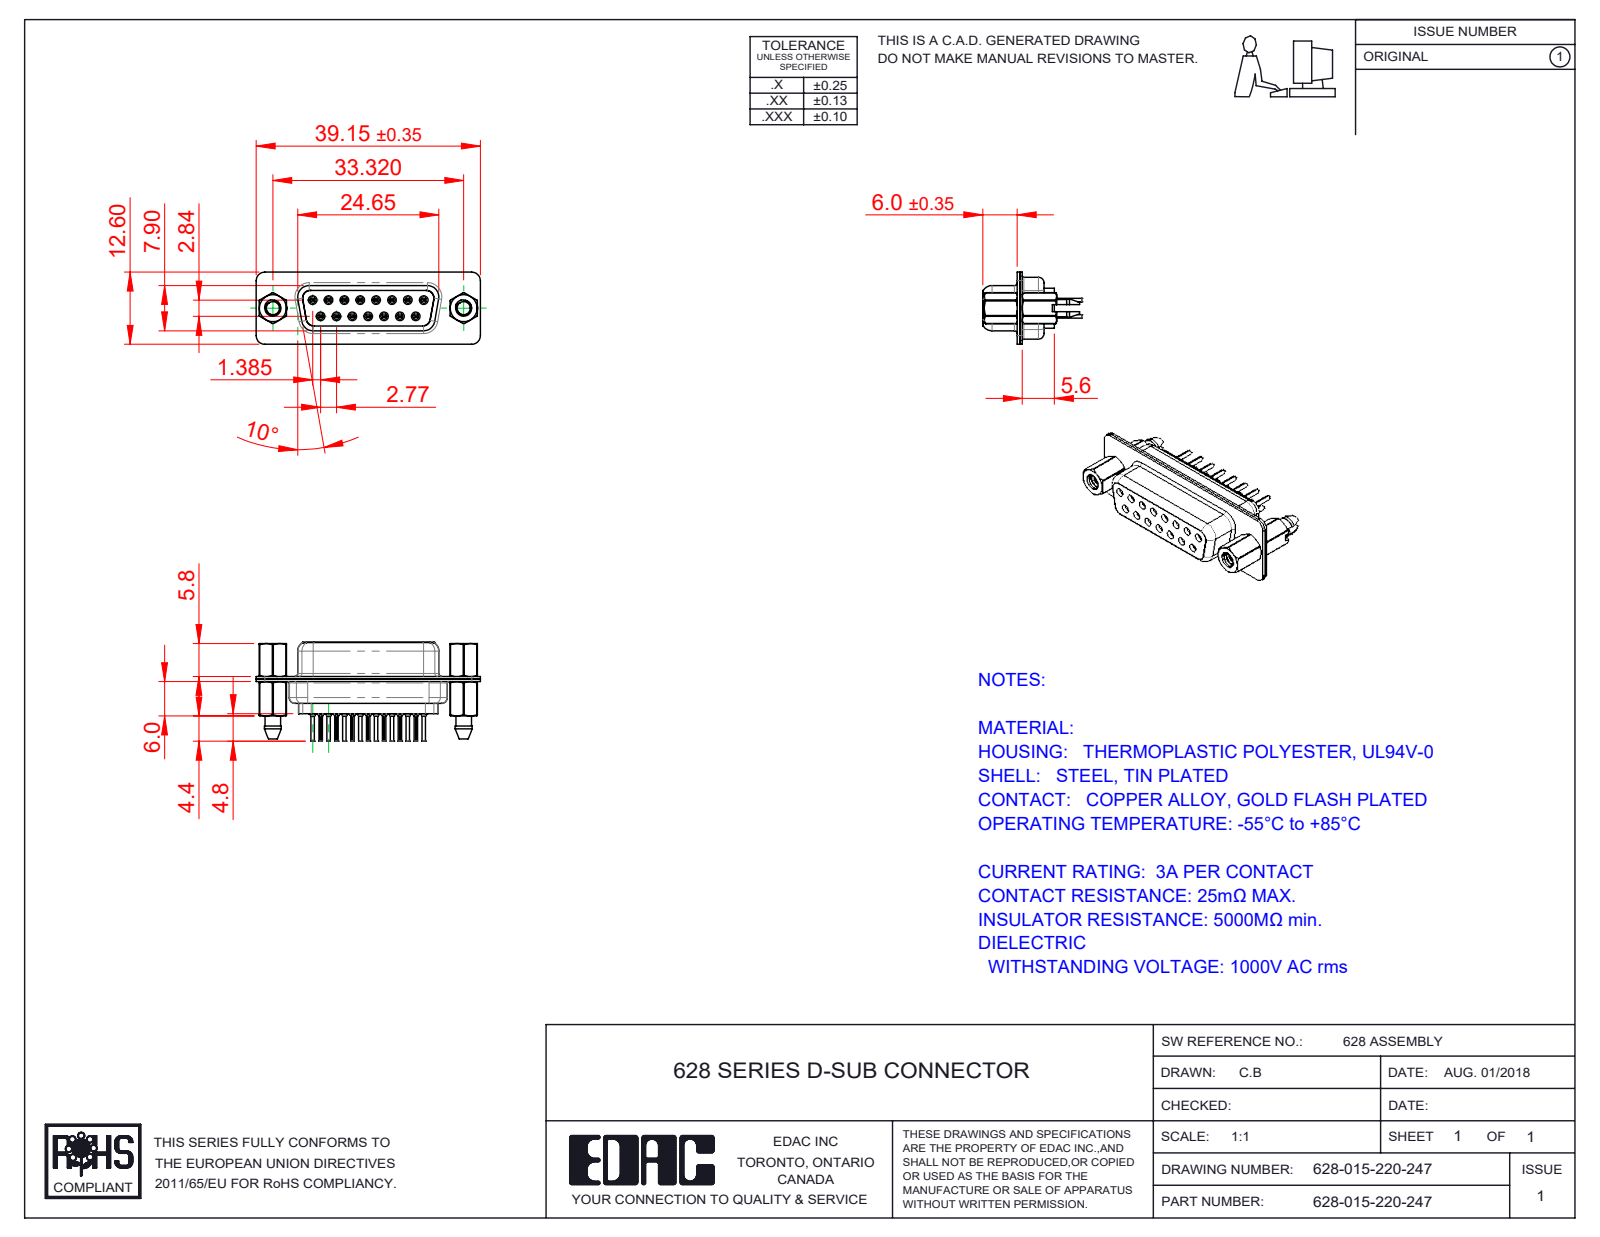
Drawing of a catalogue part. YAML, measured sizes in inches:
part_name: "628 4-40 Hex Standoff; 628 Contact Row 1_20L; 628 4-40 Threaded Boardlock_LP; 628-015-220-247 (+4 more)"
step_written_by: "SolidWorks 2020 (CONFIG_CONTROL_DESIGN)"
units: inches
bodies: {solids: 22, faces: 2384, planar: 586, cylindrical: 736, other: 1062}
overall_size: [1.541, 0.681, 0.496]
volume: 0.175
surface_area: 11.01
round_holes:
  - {diameter: 0.008, count: 15}
  - {diameter: 0.031, count: 15}
  - {diameter: 0.035, count: 15}
  - {diameter: 0.043, count: 15}
  - {diameter: 0.063, count: 15}
  - {diameter: 0.067, count: 8}
  - {diameter: 0.089, count: 2}
  - {diameter: 0.09, count: 2}
  - {diameter: 0.157, count: 2}
  - {diameter: 0.159, count: 2}
  - {diameter: 0.191, count: 2}
round_bosses_or_shafts:
  - {diameter: 0.079, count: 15}
  - {diameter: 0.059, count: 15}
  - {diameter: 0.047, count: 15}
  - {diameter: 0.024, count: 15}
  - {diameter: 0.195, count: 2}
  - {diameter: 0.189, count: 2}
  - {diameter: 0.11, count: 2}
partial_cylinders:
  - {radius: 0.004, count: 30}
  - {radius: 0.059, count: 20}
  - {radius: 0.011, count: 15}
  - {radius: 0.079, count: 12}
  - {radius: 0.053, count: 8}
  - {radius: 0.063, count: 6}
  - {radius: 0.01, count: 4}
  - {radius: 0.02, count: 4}
face_to_face_distances: [0.018, 0.016, 0.035, 0.26, 0.075, 0.335, 0.055, 0.187, 0.033, 0.278]
hole_center_spacings: [0.124, 0.109, 0.218, 0.327, 0.436, 0.198, 0.198, 0.294]
